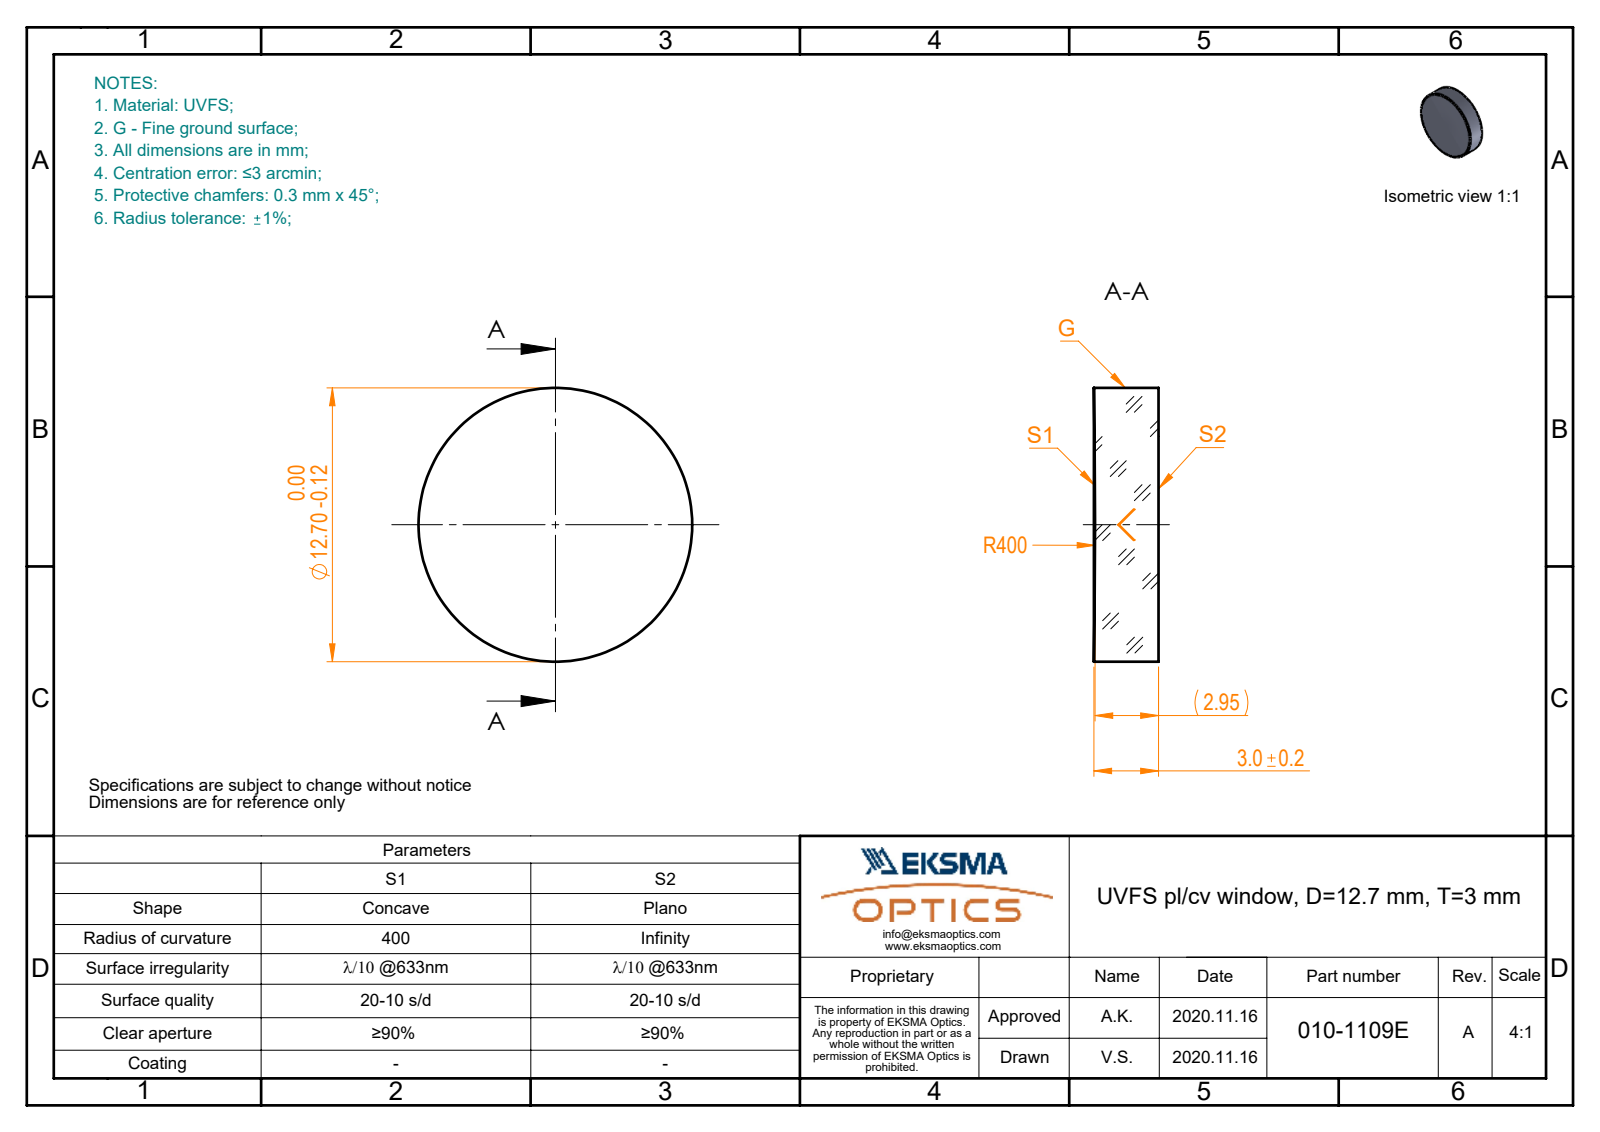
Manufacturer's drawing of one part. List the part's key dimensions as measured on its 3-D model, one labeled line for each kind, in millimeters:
Part name (STEP PRODUCT): 010-1109E_UVFS_PCV_window
STEP written by: SolidWorks 2019 (CONFIG_CONTROL_DESIGN)
Units: millimetres
Bodies: 1 solid, 5 faces (1 planar, 2 cylindrical, 2 other)
Overall size (bounding box): 12.7 × 12.7 × 3
Volume: 377 mm³ · Surface area: 373 mm²
Round bosses / shafts (diameter × count): ⌀12.7 ×1
